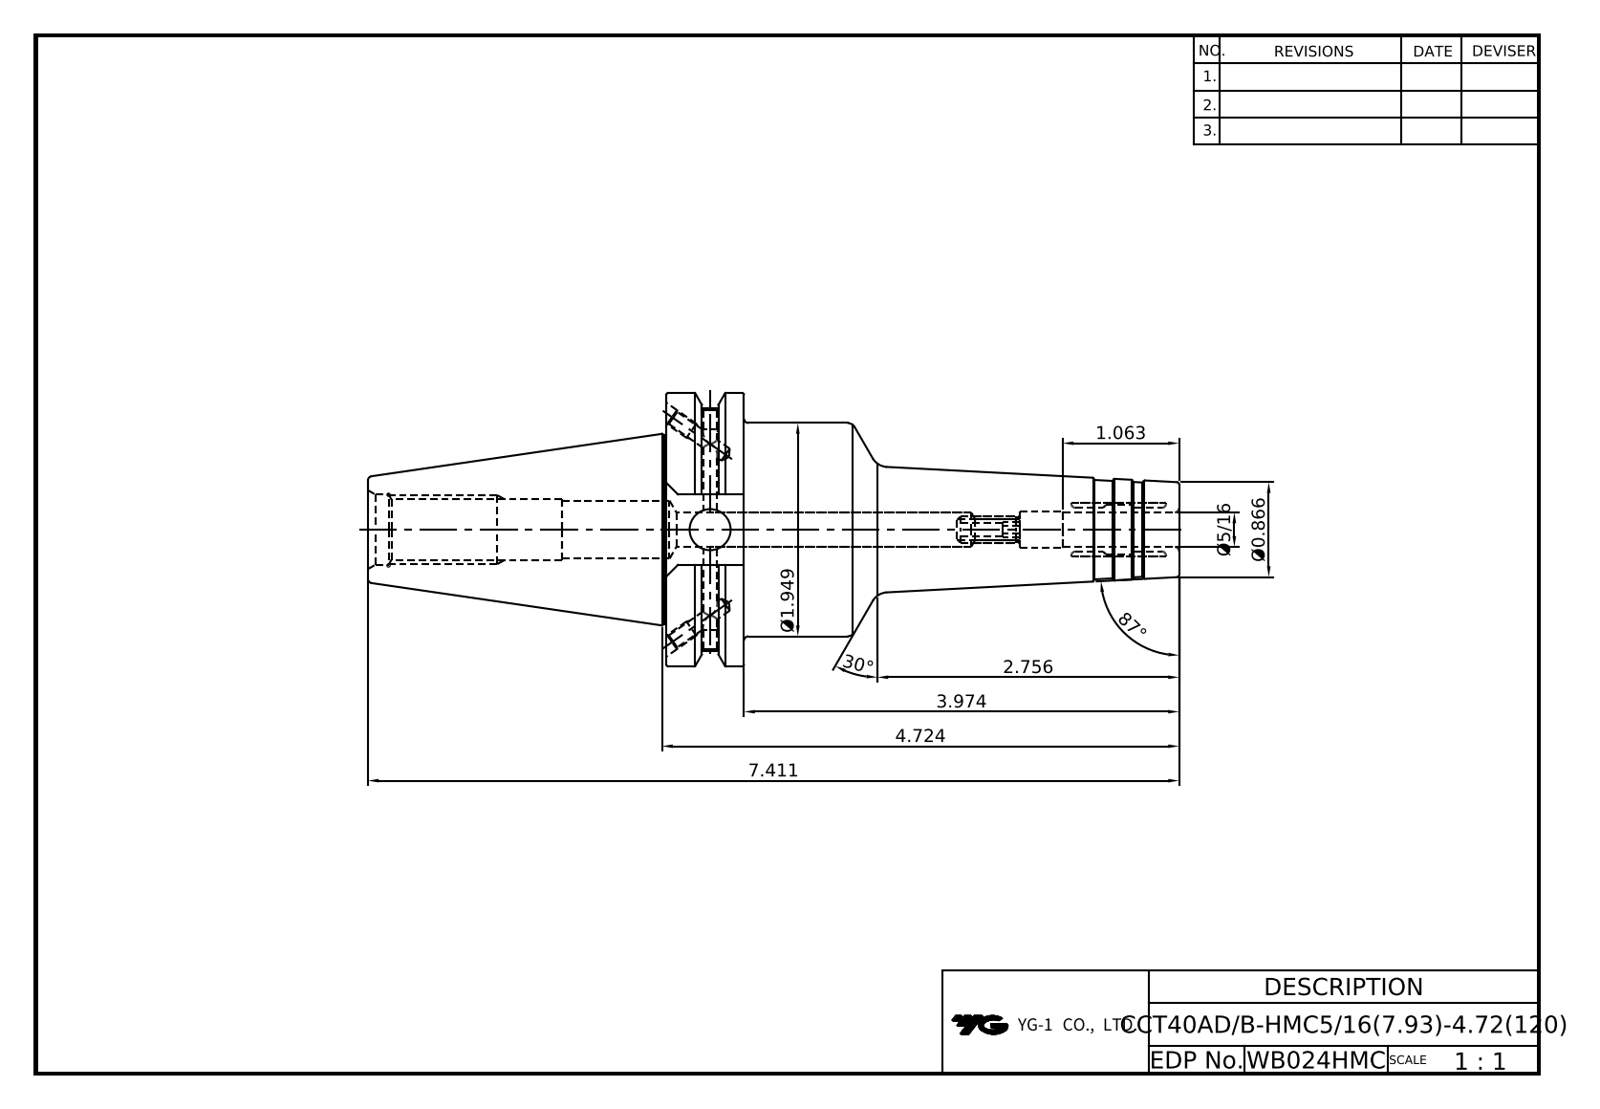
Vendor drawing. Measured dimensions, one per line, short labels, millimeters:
name: LO-CCT40ADB-HMC7.9375-120
written by: Autodesk Inventor 2025 (AUTOMOTIVE_DESIGN)
unit: mm
bodies: 1 solid, 107 faces (36 planar, 30 cylindrical, 41 other)
size: 188.25 × 63.5 × 61.09
volume: 192 071 mm³; area: 32 725 mm²
holes: 4× ⌀3.24, 2× ⌀4, 2× ⌀4.2, 1× ⌀4.92, 1× ⌀7.94, 1× ⌀8, 1× ⌀9.5, 1× ⌀9.53, 1× ⌀13, 1× ⌀13.39, 1× ⌀16.3
bosses: 1× ⌀63.5, 1× ⌀49.5
rounds: 1× R8.19, 1× R28.15
face distances: 18.05, 119, 100.95, 47.6, 16.38, 69.25, 87.3, 188.25, 81.3, 12.05
